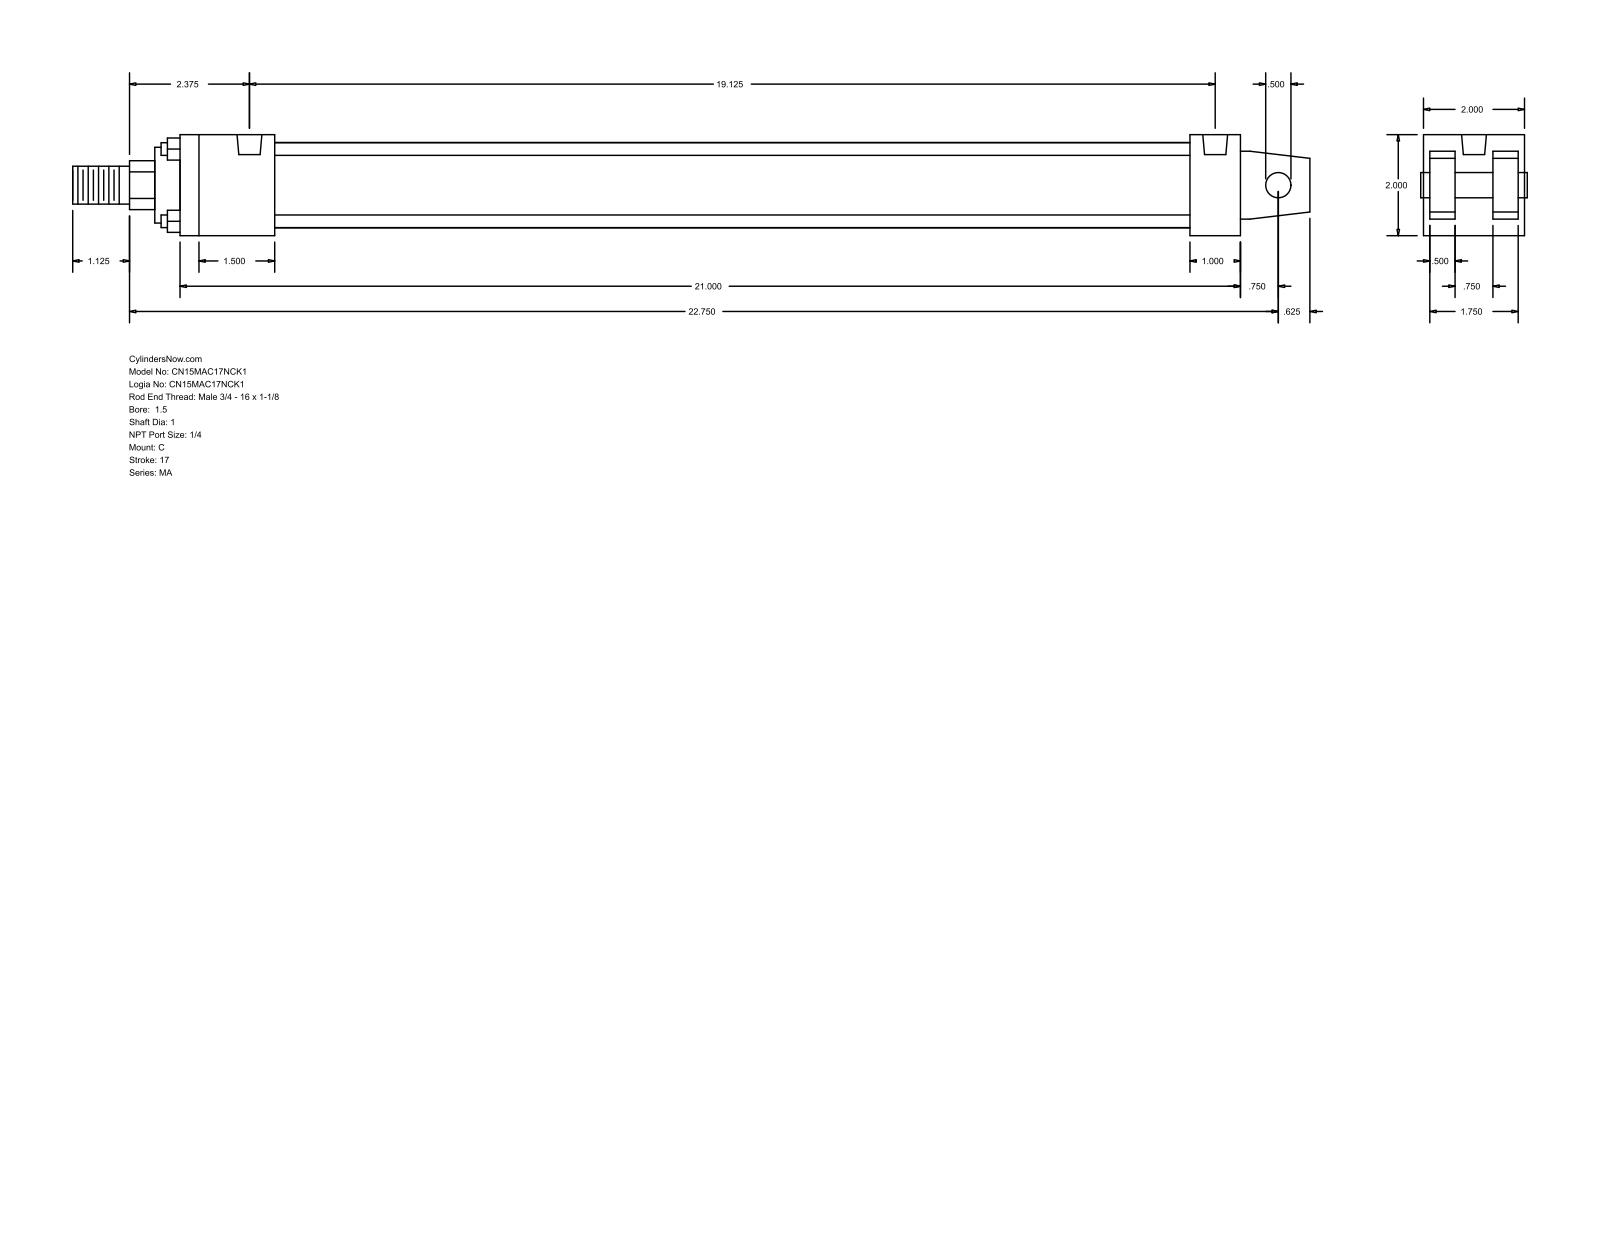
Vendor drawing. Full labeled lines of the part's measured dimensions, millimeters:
Part name (STEP PRODUCT): MA_C__0150_1
STEP written by: GSSL Pune (CONFIG_CONTROL_DESIGN)
Units: millimetres
Bodies: 0 solids, 103 faces (76 planar, 27 cylindrical, 0 other)
Overall size (bounding box): 622.3 × 50.8 × 50.8
Round holes (diameter × count): ⌀7.94 ×4, ⌀12.49 ×2
Round bosses / shafts (diameter × count): ⌀6.35 ×4, ⌀42.93 ×1, ⌀38.1 ×1, ⌀25.4 ×1, ⌀19.05 ×1, ⌀12.7 ×1
Partial cylindrical surfaces — rounded edges, fillets, slot ends (radius × count): R12.29 ×1
Main face-to-face distances: 50.8, 47.63, 12.7, 34.93, 3.17, 15.87, 31.76, 60.33, 520.7, 533.4
Hole centre spacings: 485.77
